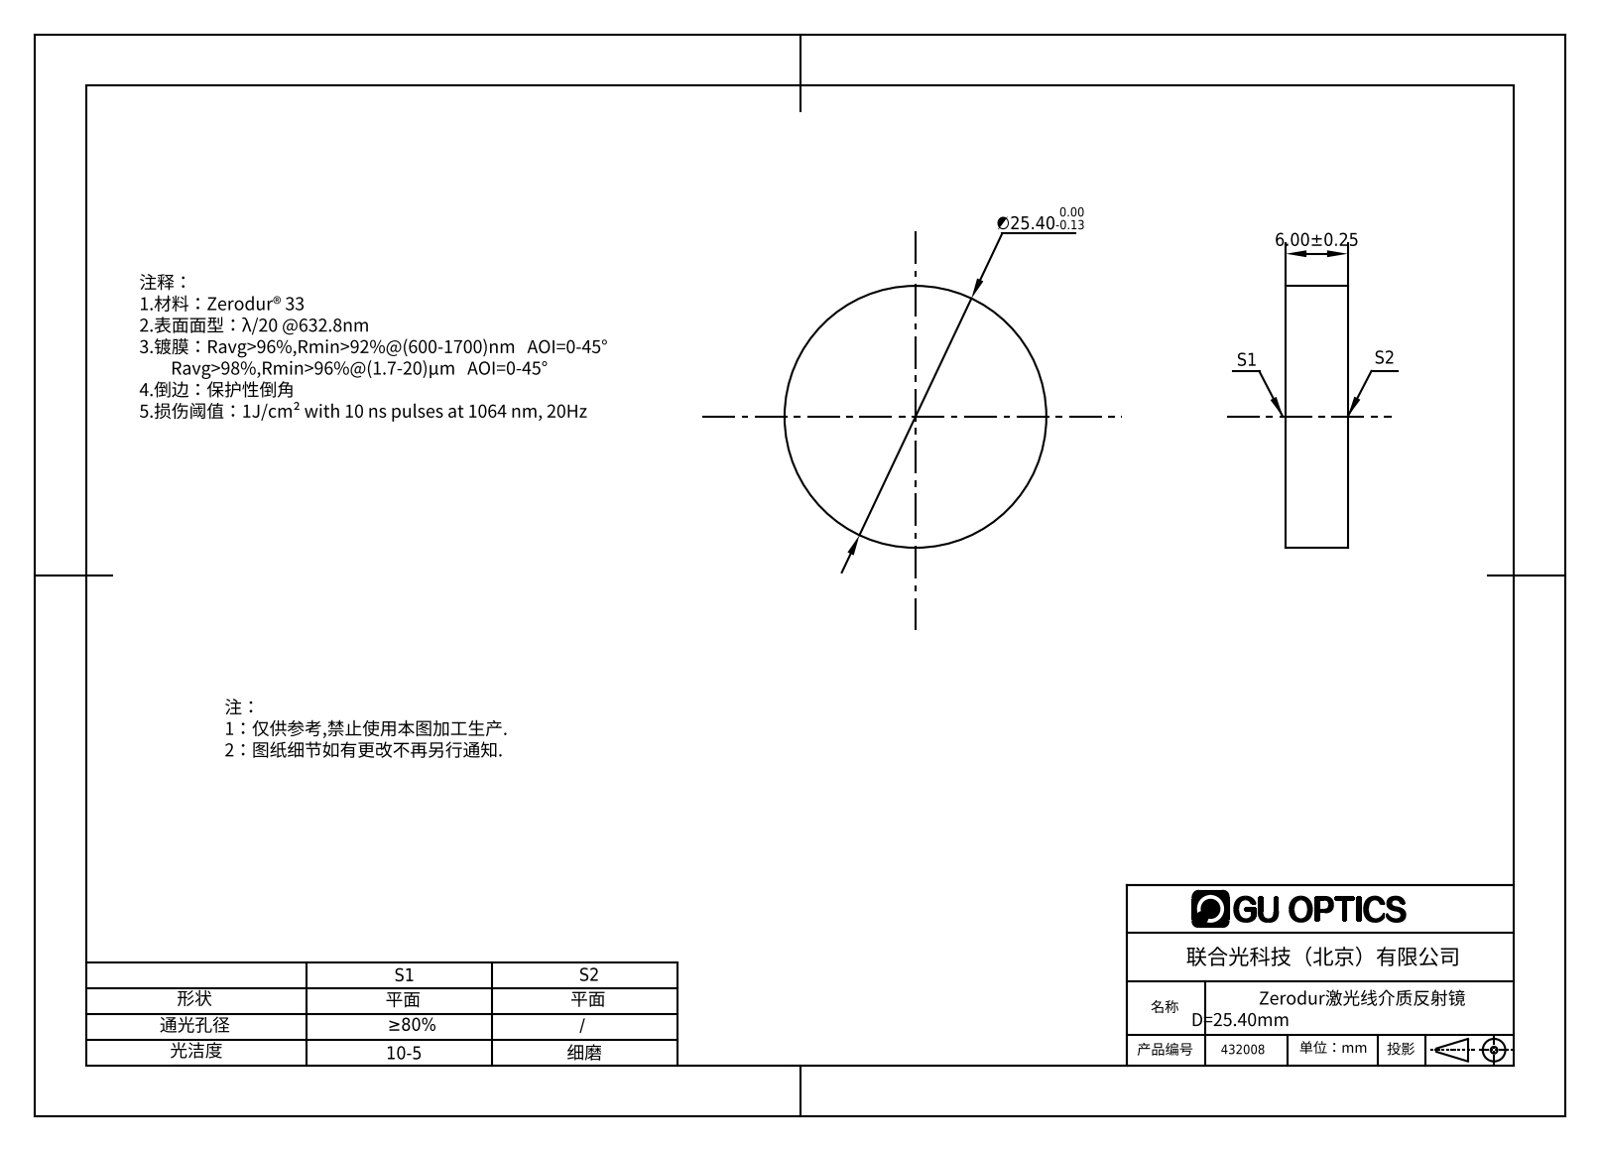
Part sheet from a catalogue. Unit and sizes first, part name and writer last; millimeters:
Units: millimetres
Overall size (bounding box): 25.4 × 25.4 × 6
Round bosses / shafts (diameter × count): ⌀25.4 ×1
Main face-to-face distances: 6
Volume: 3 040 mm³ · Surface area: 1 492 mm²
Bodies: 1 solid, 4 faces (2 planar, 2 cylindrical, 0 other)
Part name (STEP PRODUCT): 432000
STEP written by: SolidWorks 2016 (AUTOMOTIVE_DESIGN)
